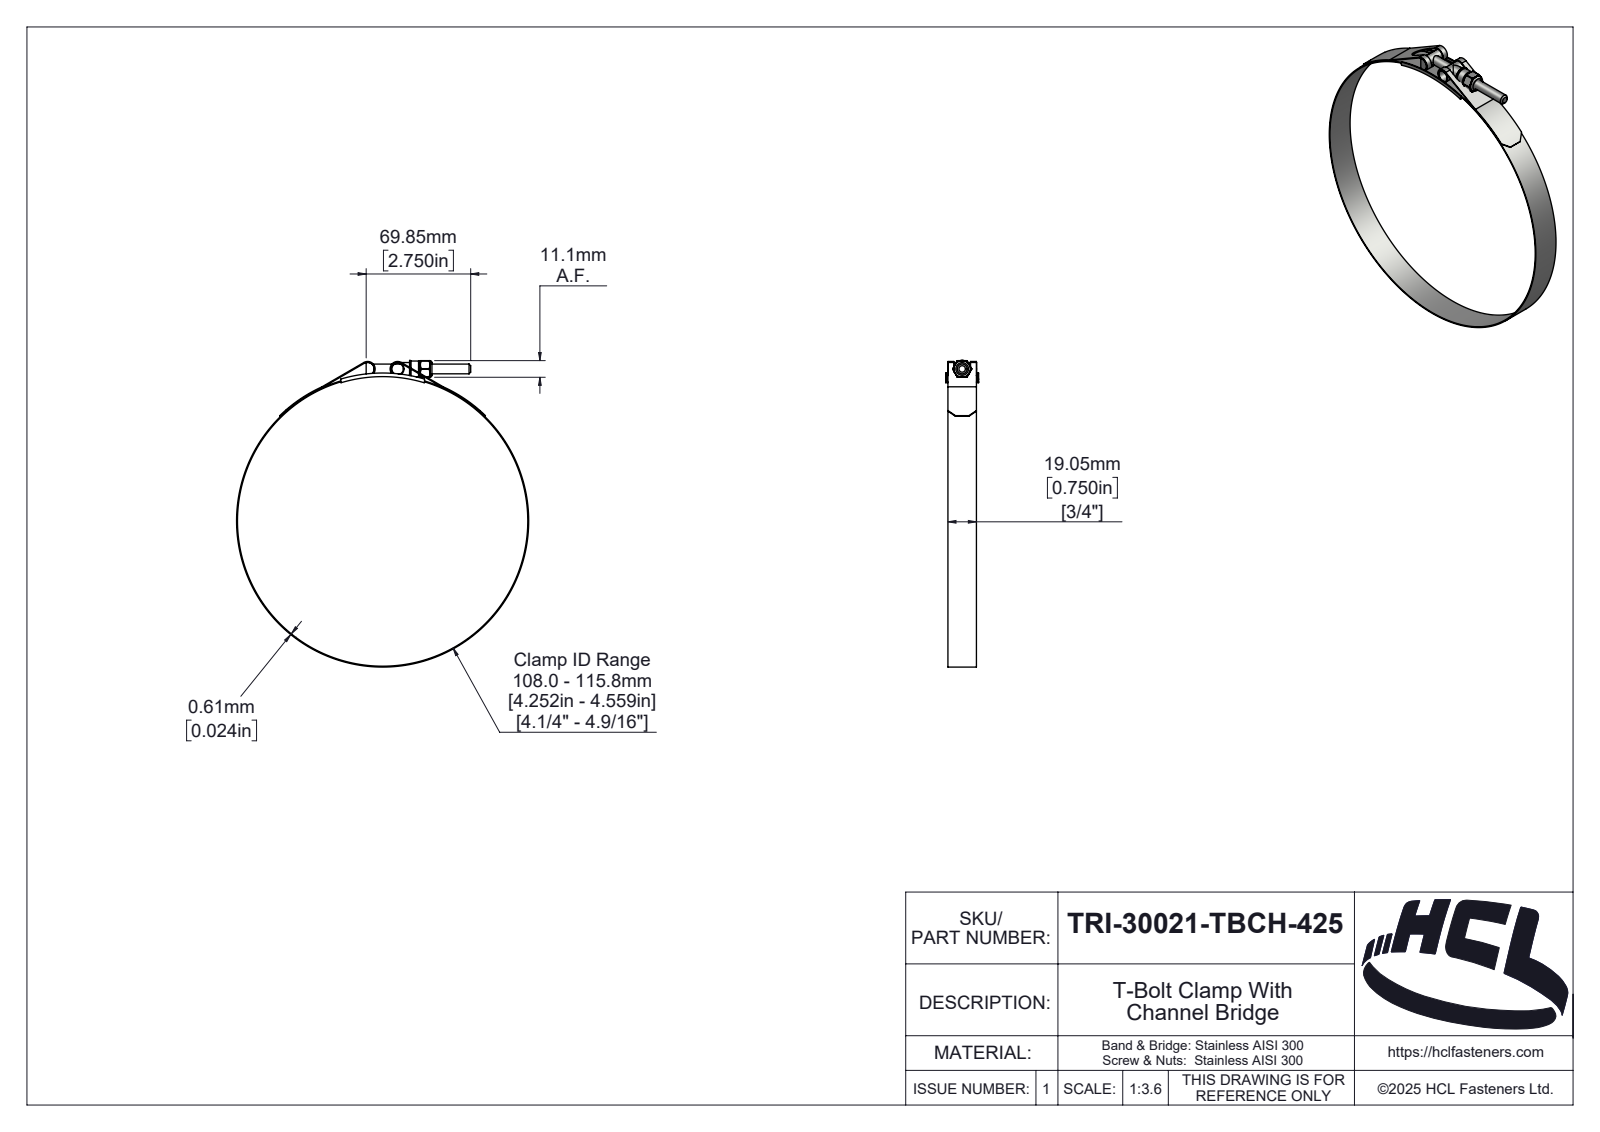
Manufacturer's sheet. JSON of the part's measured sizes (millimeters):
{"part_name": "TRI-30021-TBCH-425", "step_written_by": "SolidWorks 2025 (AUTOMOTIVE_DESIGN)", "units": "millimeters", "bodies": {"solids": 6, "faces": 330, "planar": 46, "cylindrical": 122, "other": 162}, "overall_size": [204.84, 195.22, 22], "volume_mm3": 13461, "surface_area_mm2": 35885, "round_holes": [[5.4, 1], [6.35, 1], [6.5, 1], [7.58, 1], [194, 1]], "round_bosses_or_shafts": [[8.58, 2], [195.22, 1], [10.58, 1]], "partial_cylinders_radius": [[0.39, 6], [0.5, 2], [4.39, 2], [5, 2], [0.59, 1], [2.42, 1], [3.03, 1], [3.19, 1]], "face_to_face_distances": [0.61, 19.06, 1.47, 20.53, 21.39, 0.86, 19.92, 0.74, 22, 11.11], "hole_center_spacings": [102]}
